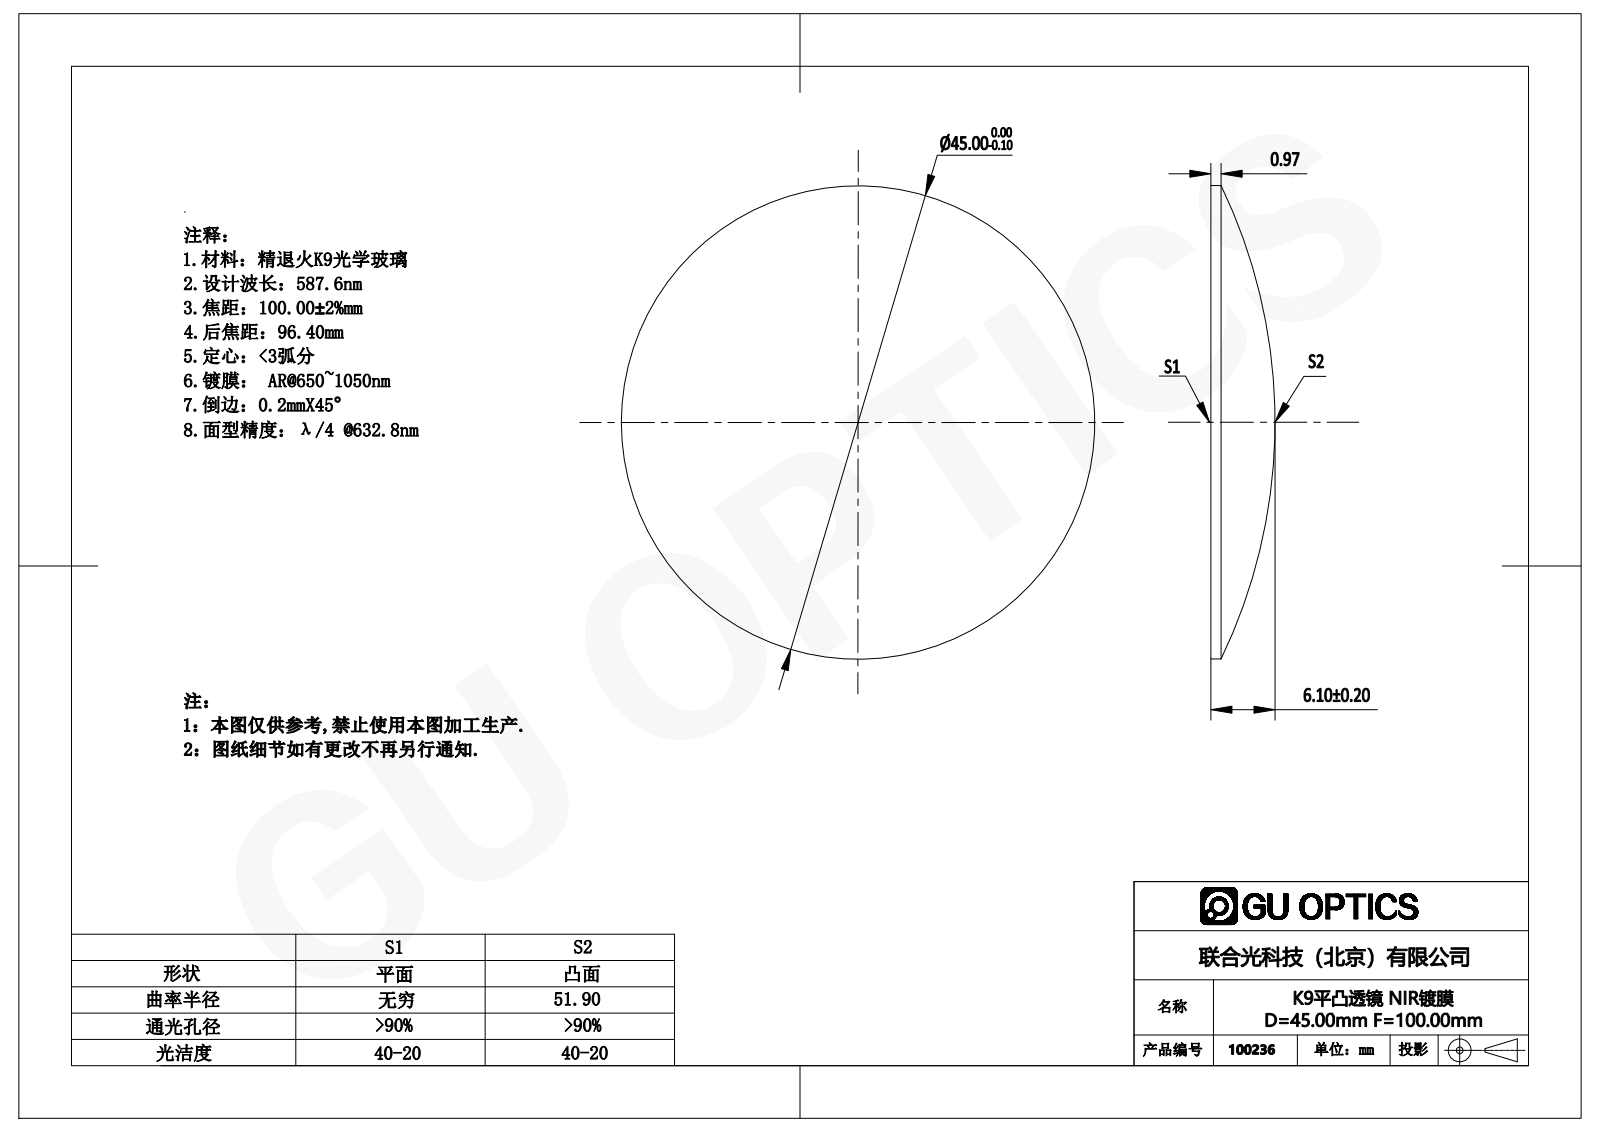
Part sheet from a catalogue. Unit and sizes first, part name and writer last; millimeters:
Units: millimetres
Overall size (bounding box): 45 × 45 × 6.1
Round bosses / shafts (diameter × count): ⌀45 ×1
Volume: 5 693 mm³ · Surface area: 3 401 mm²
Bodies: 1 solid, 5 faces (1 planar, 2 cylindrical, 2 other)
Part name (STEP PRODUCT): 100236
STEP written by: SolidWorks 2016 (AUTOMOTIVE_DESIGN)
